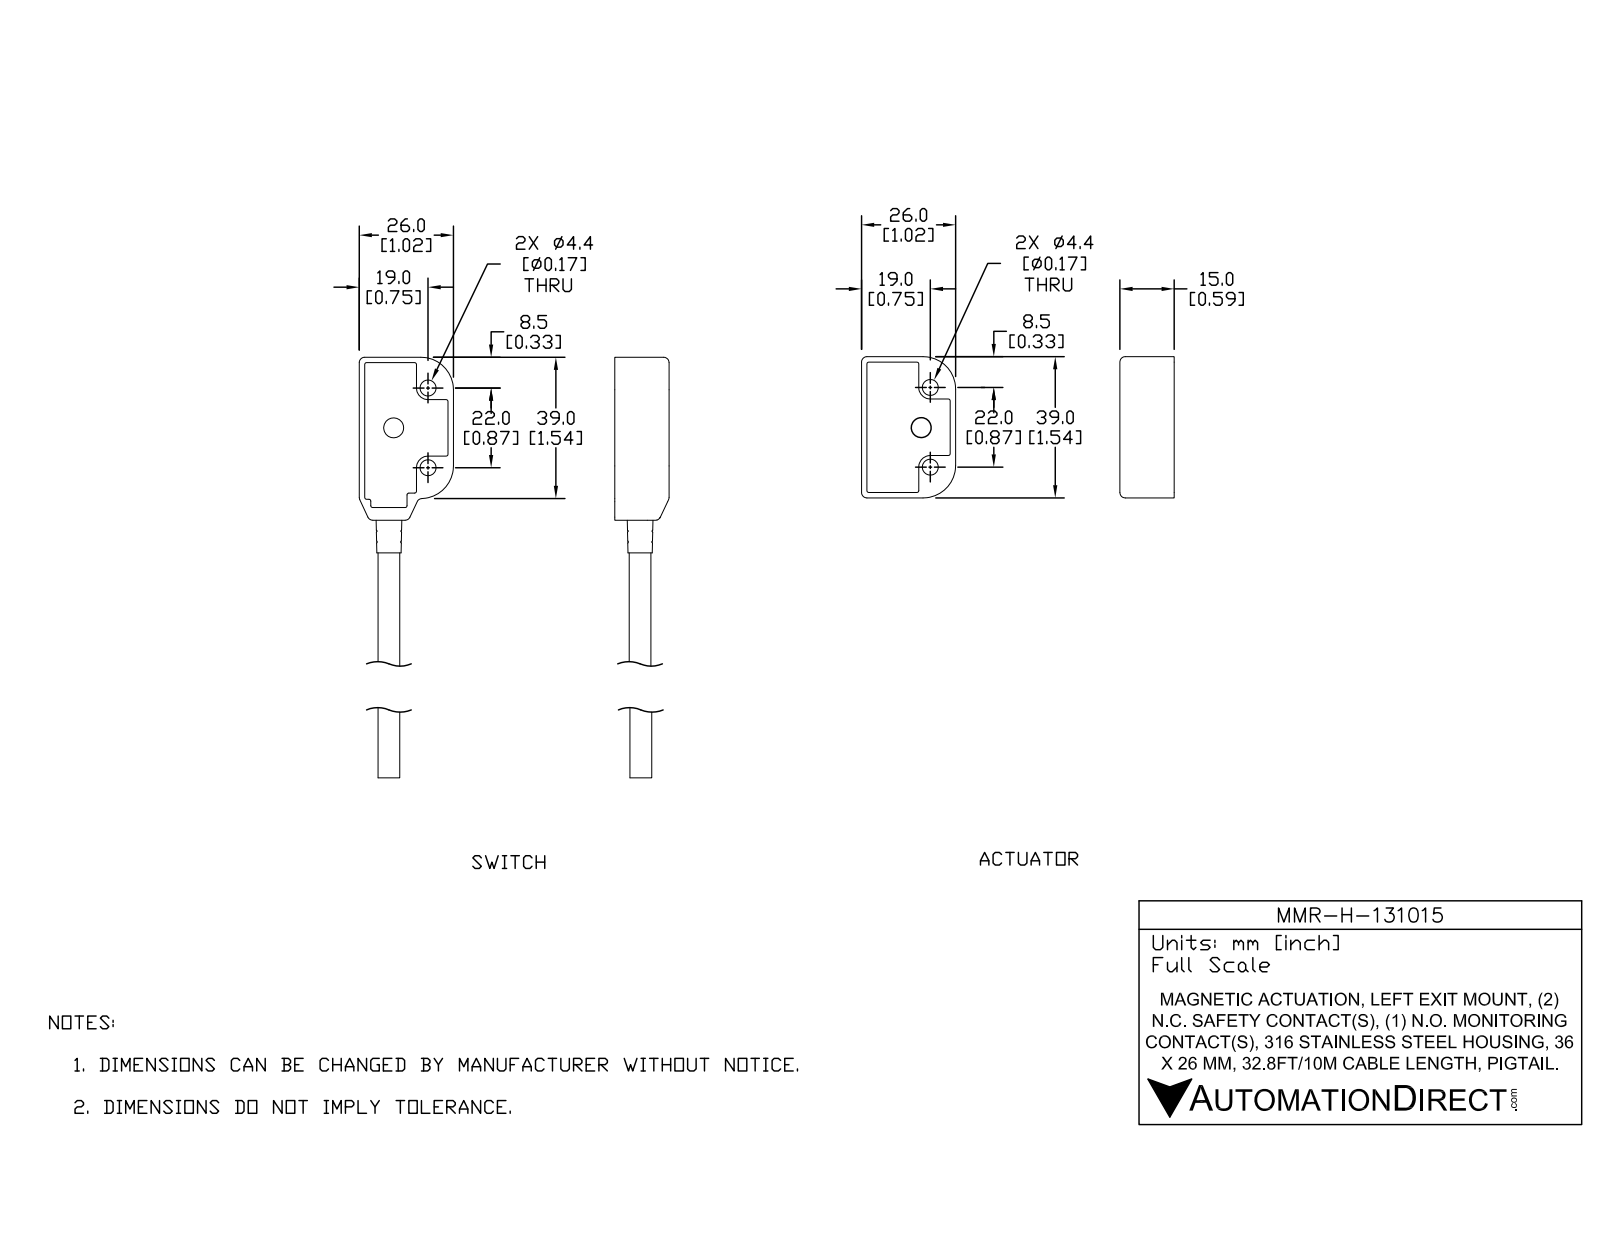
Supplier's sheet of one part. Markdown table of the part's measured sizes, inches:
| quantity | value |
| --- | --- |
| part name | MMR-H-131015_2; MMR-H-131015_1; MMR-H-131015 |
| STEP written by | SolidWorks 2017 (AUTOMOTIVE_DESIGN) |
| units | inches |
| bodies | 8 solids, 590 faces (175 planar, 226 cylindrical, 189 other) |
| overall size | 7.803 × 2.087 × 0.591 |
| volume | 1.231 in³ |
| surface area | 30.87 in² |
| round holes (diameter × count) | 0.173 × 4, 0.197 × 2, 0.118 × 1, 0.232 × 1, 0.283 × 1 |
| round bosses / shafts (diameter × count) | 0.079 × 2, 0.339 × 1, 0.299 × 1, 0.28 × 1, 0.236 × 1 |
| partial cylindrical surfaces (radius × count) | 0.02 × 83, 0.012 × 26, 0.059 × 15, 0.008 × 8, 0.157 × 6, 0.126 × 4, 0.13 × 4, 0.181 × 4 |
| main face-to-face distances | 0.059, 0.575, 0.516, 0.098, 0.461, 0.52, 0.055, 0.591, 0.531, 0.965 |
| hole center spacings | 0.572, 0.866, 1.239, 1.535, 1.763, 0.076, 0.44, 0.448 |
